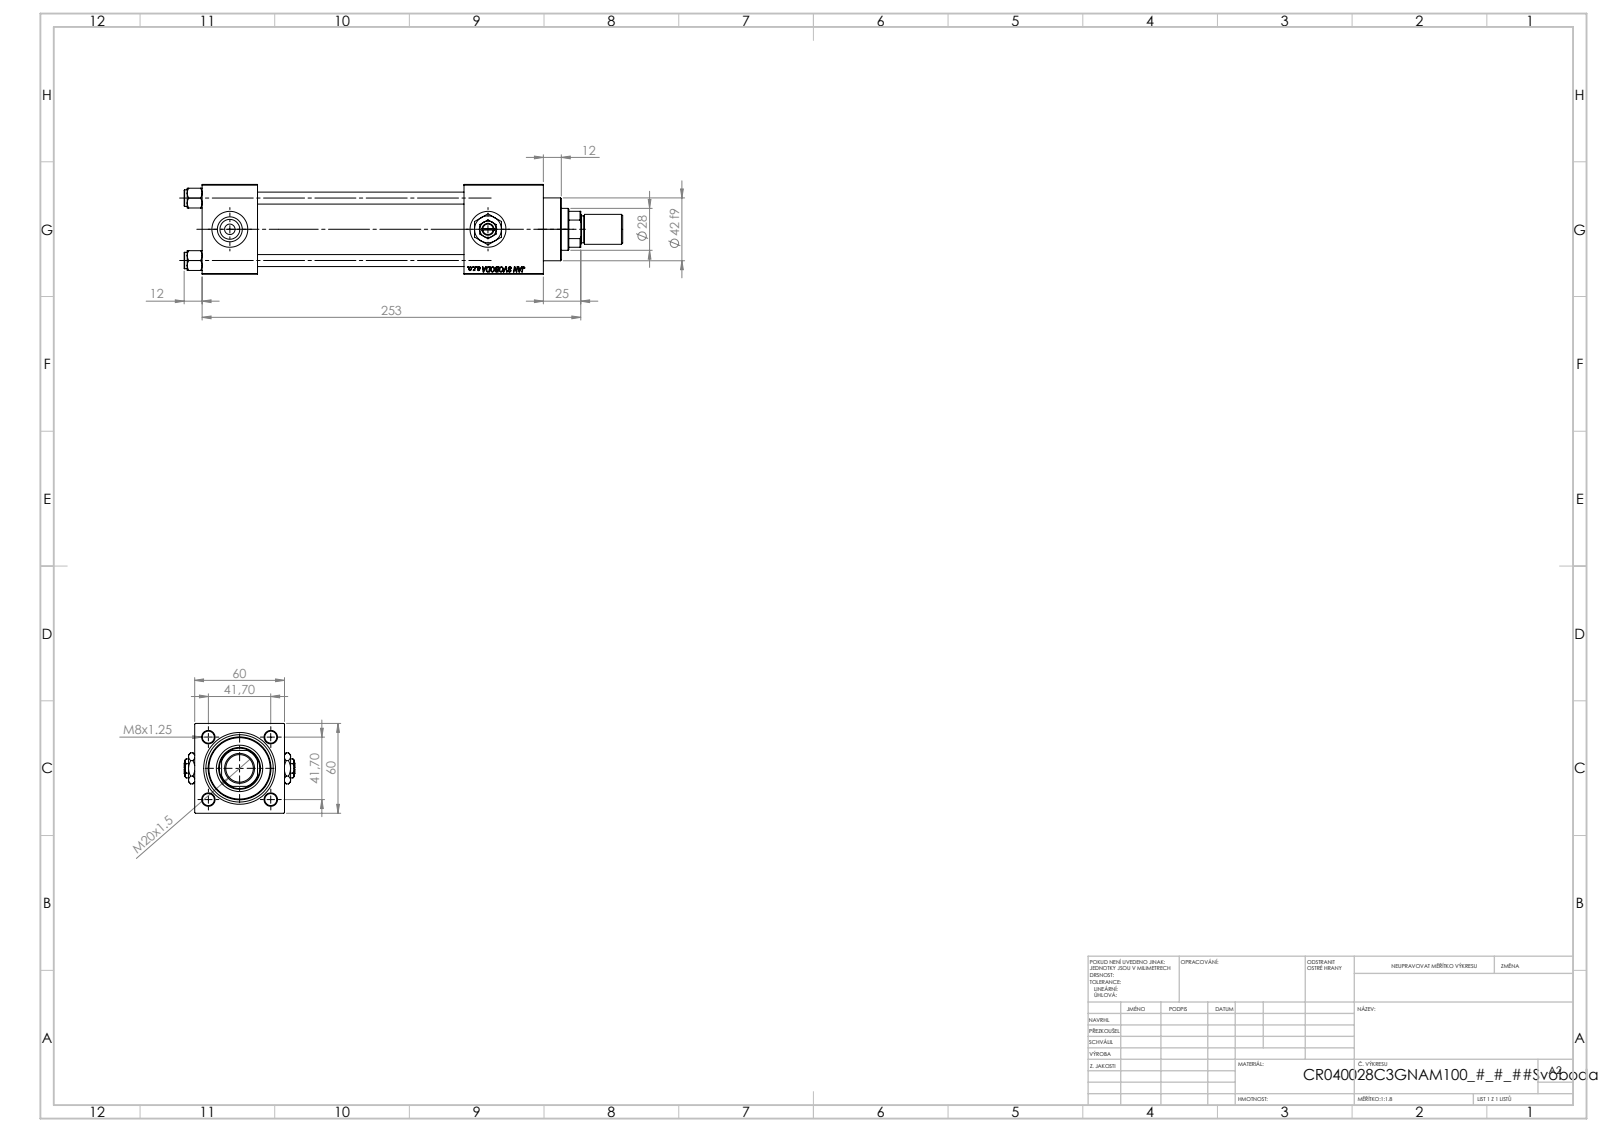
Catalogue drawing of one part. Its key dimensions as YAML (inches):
part_name: "NUT_M5_C; V215CR_C_TYCINKA; ROD_END_AH; V215_VC_A (+3 more)"
step_written_by: "SolidWorks 2019 (CONFIG_CONTROL_DESIGN)"
units: inches
bodies: {solids: 14, faces: 1264, planar: 578, cylindrical: 102, other: 584}
overall_size: [11.535, 2.913, 2.362]
volume: 32.18
surface_area: 237.9
round_holes:
  - {diameter: 0.315, count: 4}
  - {diameter: 0.276, count: 2}
  - {diameter: 0.656, count: 2}
  - {diameter: 0.945, count: 2}
  - {diameter: 0.728, count: 1}
  - {diameter: 1.102, count: 1}
  - {diameter: 1.22, count: 1}
  - {diameter: 1.575, count: 1}
  - {diameter: 1.772, count: 1}
round_bosses_or_shafts:
  - {diameter: 0.433, count: 4}
  - {diameter: 1.811, count: 1}
  - {diameter: 1.654, count: 1}
  - {diameter: 0.787, count: 1}
  - {diameter: 0.709, count: 1}
partial_cylinders:
  - {radius: 0.531, count: 1}
face_to_face_distances: [2.362, 1.457, 6.89, 5.433, 2.087, 7.846, 6.39, 0.957, 8.976, 7.52]
hole_center_spacings: [1.161, 1.642, 2.322, 6.791]
